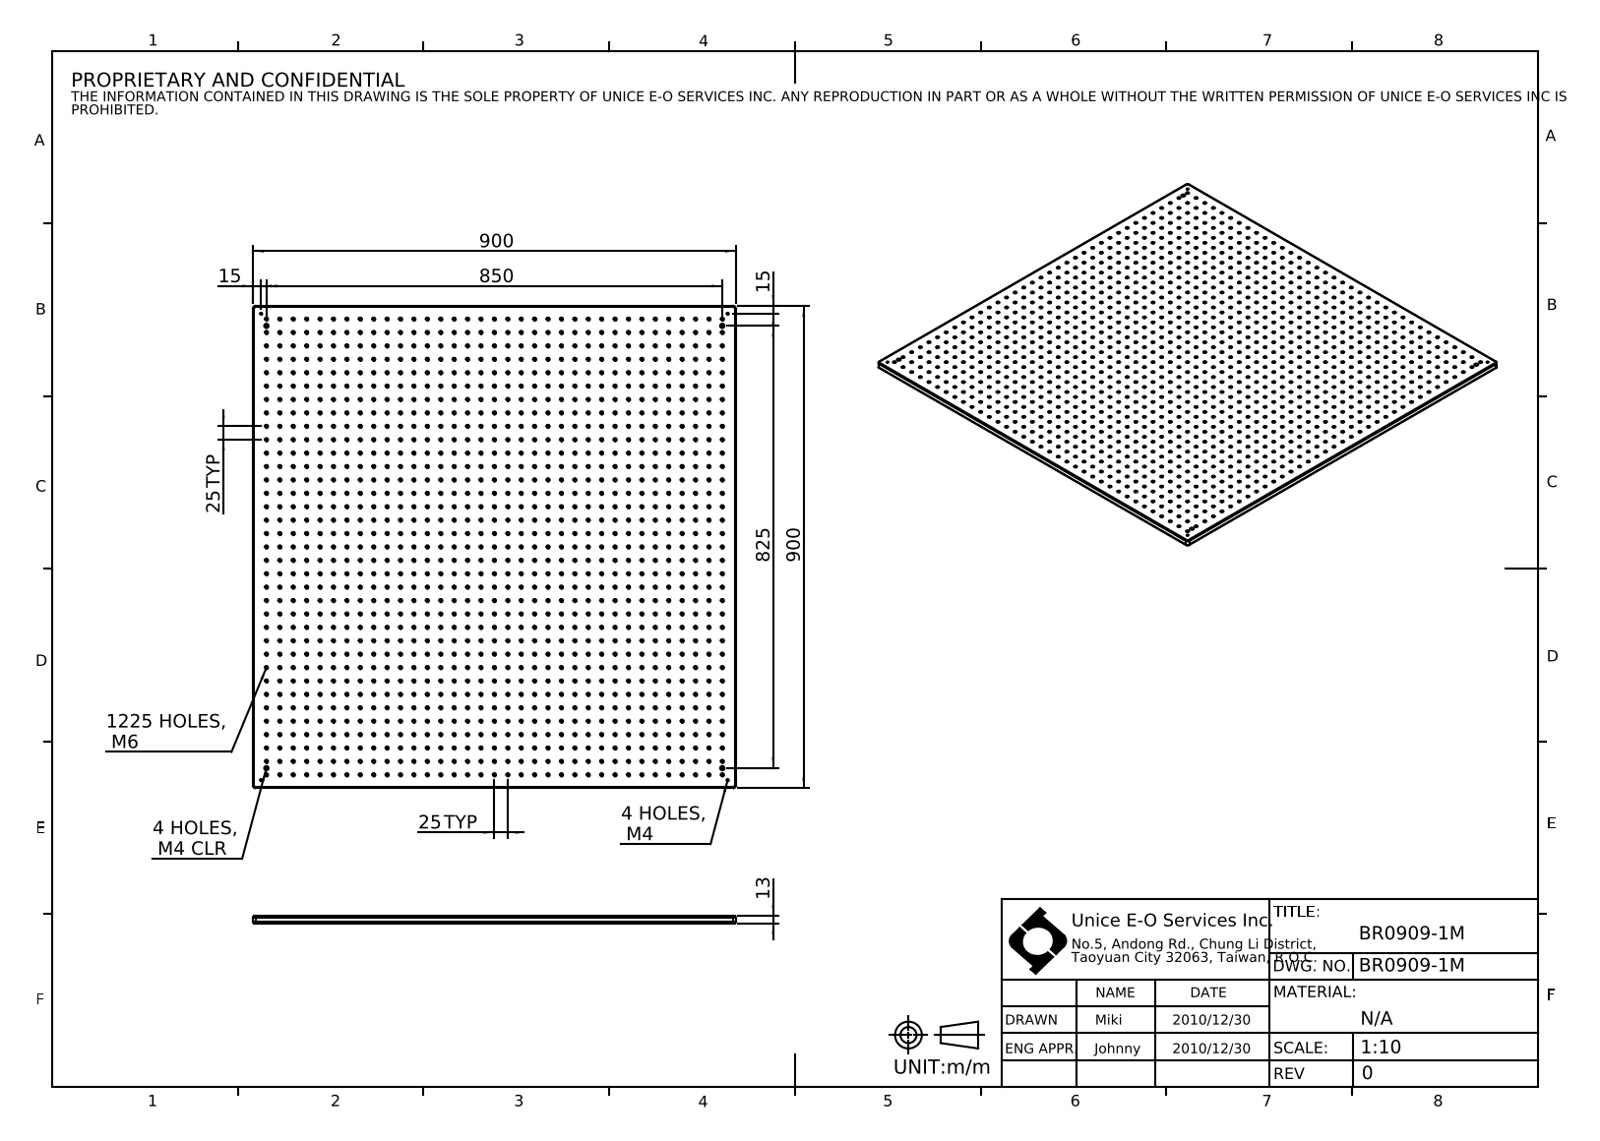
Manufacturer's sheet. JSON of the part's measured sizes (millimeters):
{"part_name": "BR0909-1M", "step_written_by": "SolidWorks 2016 (CONFIG_CONTROL_DESIGN)", "units": "millimeters", "bodies": {"solids": 1, "faces": 2504, "planar": 10, "cylindrical": 2486, "other": 8}, "overall_size": [900, 900, 13], "volume_mm3": 10210000, "surface_area_mm2": 1864000, "round_holes": [[5, 1225], [3.3, 4], [4.5, 4], [8, 4]], "partial_cylinders_radius": [[2, 8], [5, 4]], "face_to_face_distances": [13, 900, 7, 6], "hole_center_spacings": [25, 50, 75, 100, 125, 150, 175, 200]}
